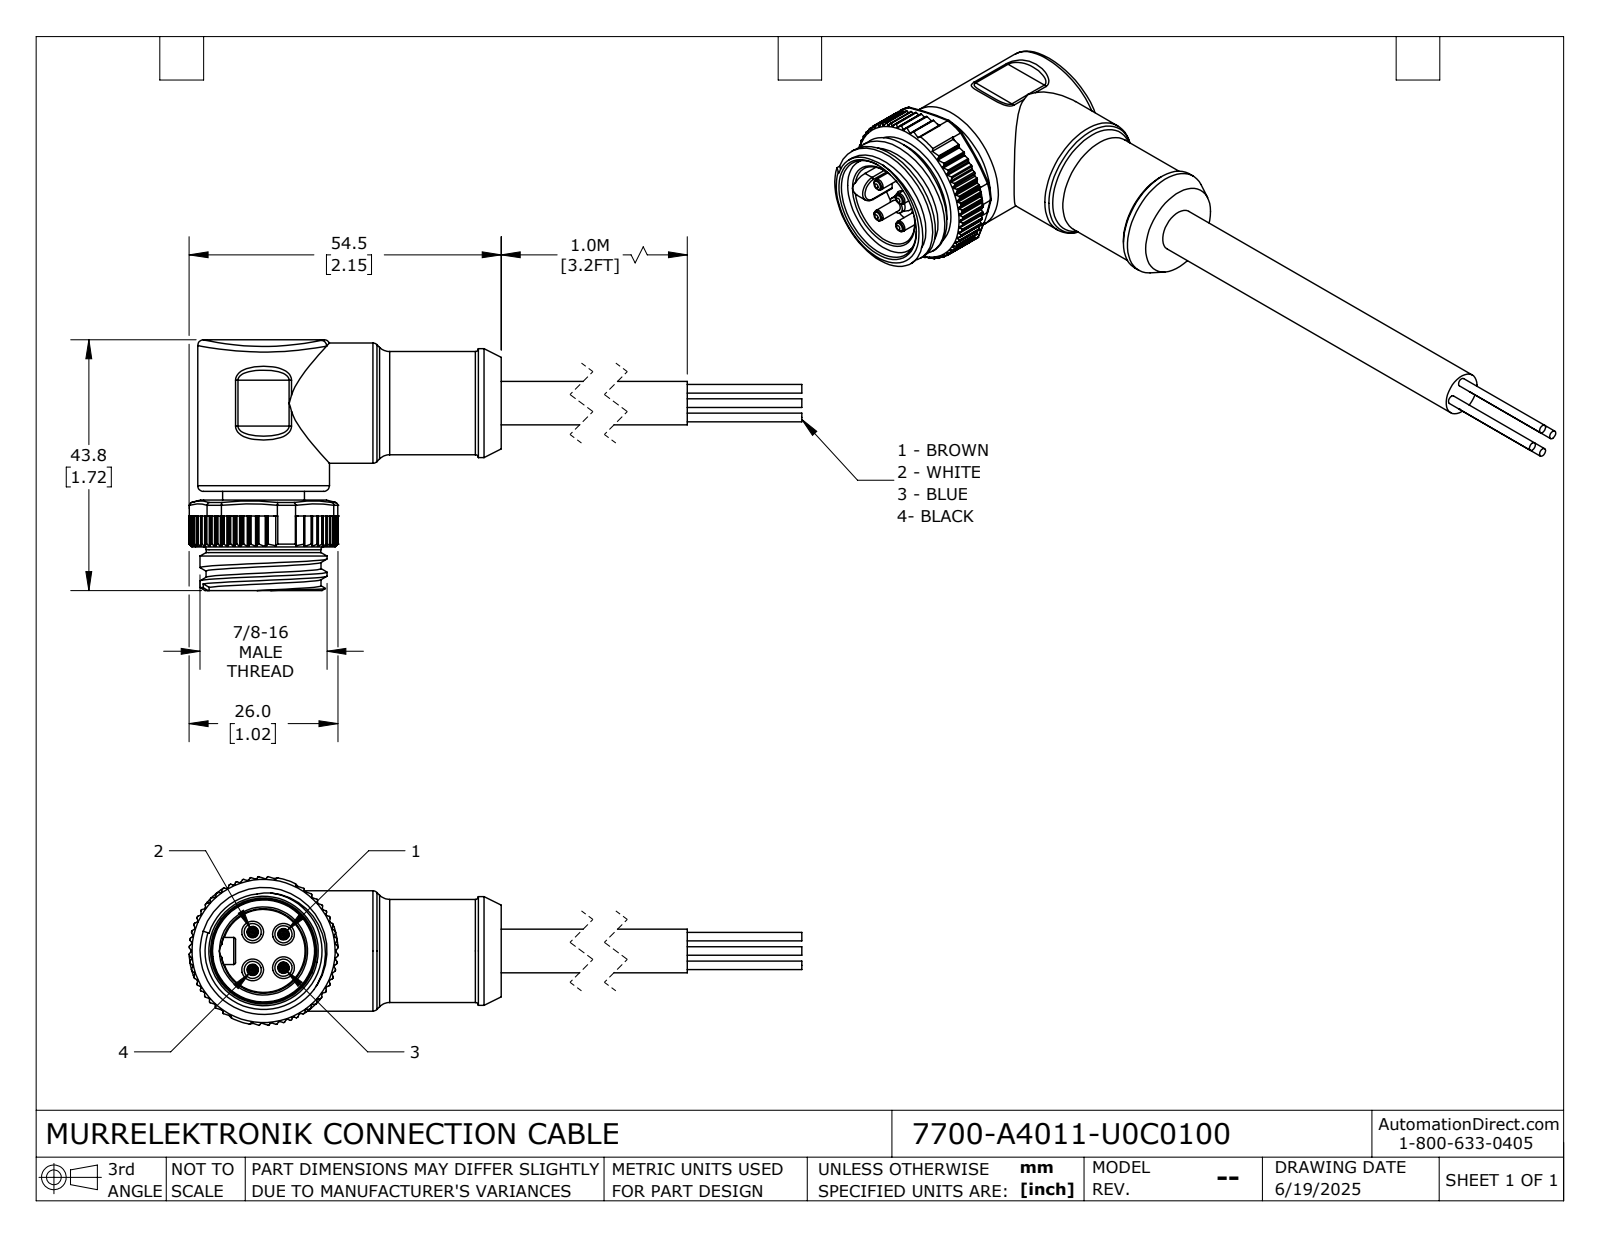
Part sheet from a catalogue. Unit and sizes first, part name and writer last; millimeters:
Units: millimetres
Overall size (bounding box): 144.49 × 43.76 × 25.95
Round holes (diameter × count): ⌀15.6 ×1, ⌀18.5 ×1
Round bosses / shafts (diameter × count): ⌀3 ×4, ⌀2 ×4, ⌀1.5 ×4, ⌀23 ×1, ⌀22.17 ×1, ⌀21 ×1, ⌀20.05 ×1, ⌀20 ×1
Partial cylindrical surfaces — rounded edges, fillets, slot ends (radius × count): R0.2 ×126, R0.3 ×18, R0.1 ×4, R0.7 ×4, R1 ×4, R2.5 ×4, R2.35 ×1, R13 ×1
Main face-to-face distances: 1.5, 8.2, 9.7, 0.9, 7.3, 8.8, 15.8, 21, 14.3, 6.1
Volume: 28 280 mm³ · Surface area: 10 856 mm²
Bodies: 1 solid, 604 faces (238 planar, 282 cylindrical, 84 other)
Part name (STEP PRODUCT): 7700-A4011-U0C0100
STEP written by: SolidWorks 2024 (CONFIG_CONTROL_DESIGN)
